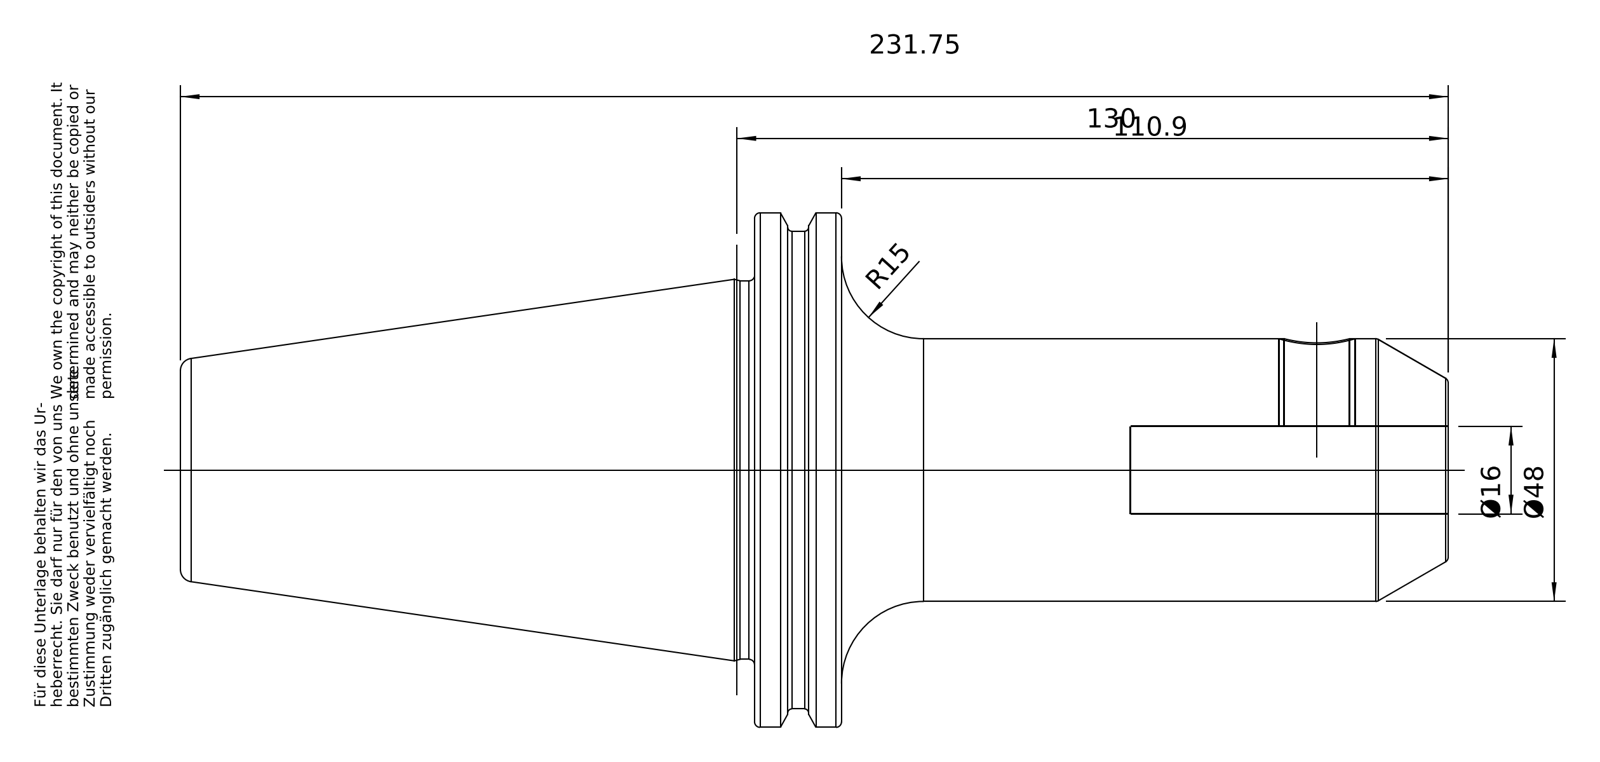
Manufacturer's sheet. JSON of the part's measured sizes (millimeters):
{"part_name": "50-304-16", "step_written_by": "PRO/ENGINEER BY PARAMETRIC TECHNOLOGY CORPORATION, 2010430 (CONFIG_CONTROL_DESIGN)", "units": "millimeters", "bodies": {"solids": 1, "faces": 104, "planar": 22, "cylindrical": 32, "other": 50}, "overall_size": [231.6, 97.47, 94], "volume_mm3": 528300, "surface_area_mm2": 61533, "round_holes": [[12, 1], [14, 1], [16, 1], [20.75, 1], [25.01, 1], [25.7, 1]], "round_bosses_or_shafts": [[91, 1], [69.15, 1], [48, 1], [24.01, 1]], "partial_cylinders_radius": [[1.75, 5], [48.74, 1]], "face_to_face_distances": [15.85, 126.8, 110.95, 104.8, 120.65, 231.6, 72.8, 25.8, 173.5, 68.7]}
